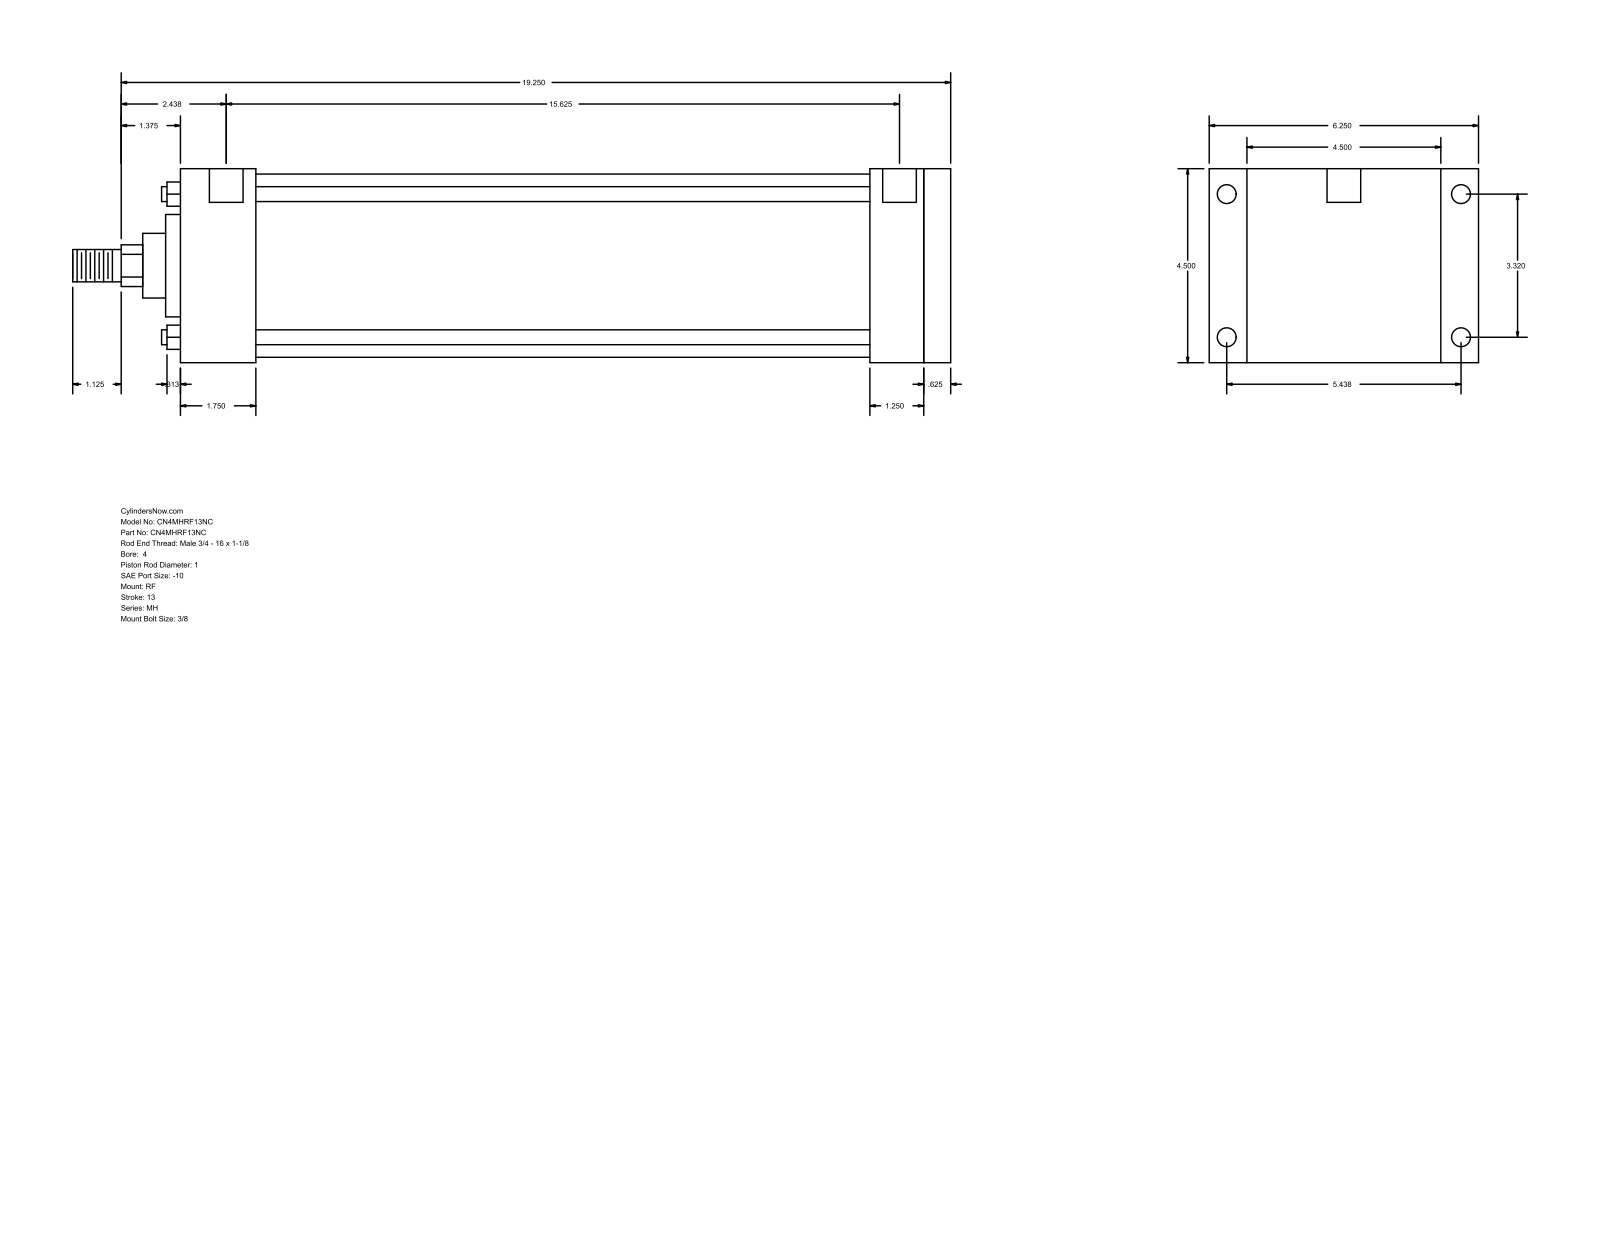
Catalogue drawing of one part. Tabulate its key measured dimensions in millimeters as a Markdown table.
| quantity | value |
| --- | --- |
| part name | MH_RF__0400_1 |
| STEP written by | GSSL Pune (CONFIG_CONTROL_DESIGN) |
| units | millimeters |
| bodies | 0 solids, 94 faces (65 planar, 29 cylindrical, 0 other) |
| overall size | 517.52 × 158.75 × 114.3 |
| round holes (diameter × count) | 8.73 × 4, 11.13 × 4, 19.84 × 2 |
| round bosses / shafts (diameter × count) | 8.76 × 4, 107.95 × 1, 60.33 × 1, 38.1 × 1, 25.4 × 1, 19.05 × 1 |
| partial cylindrical surfaces (radius × count) | 12.29 × 1 |
| main face-to-face distances | 114.3, 454.03, 438.15, 15.88, 47.63, 44.46, 393.69, 409.57, 406.4, 361.94 |
| hole center spacings | 84.32, 138.12, 161.82, 400.05, 1.58, 1.59, 396.88, 398.46 |
